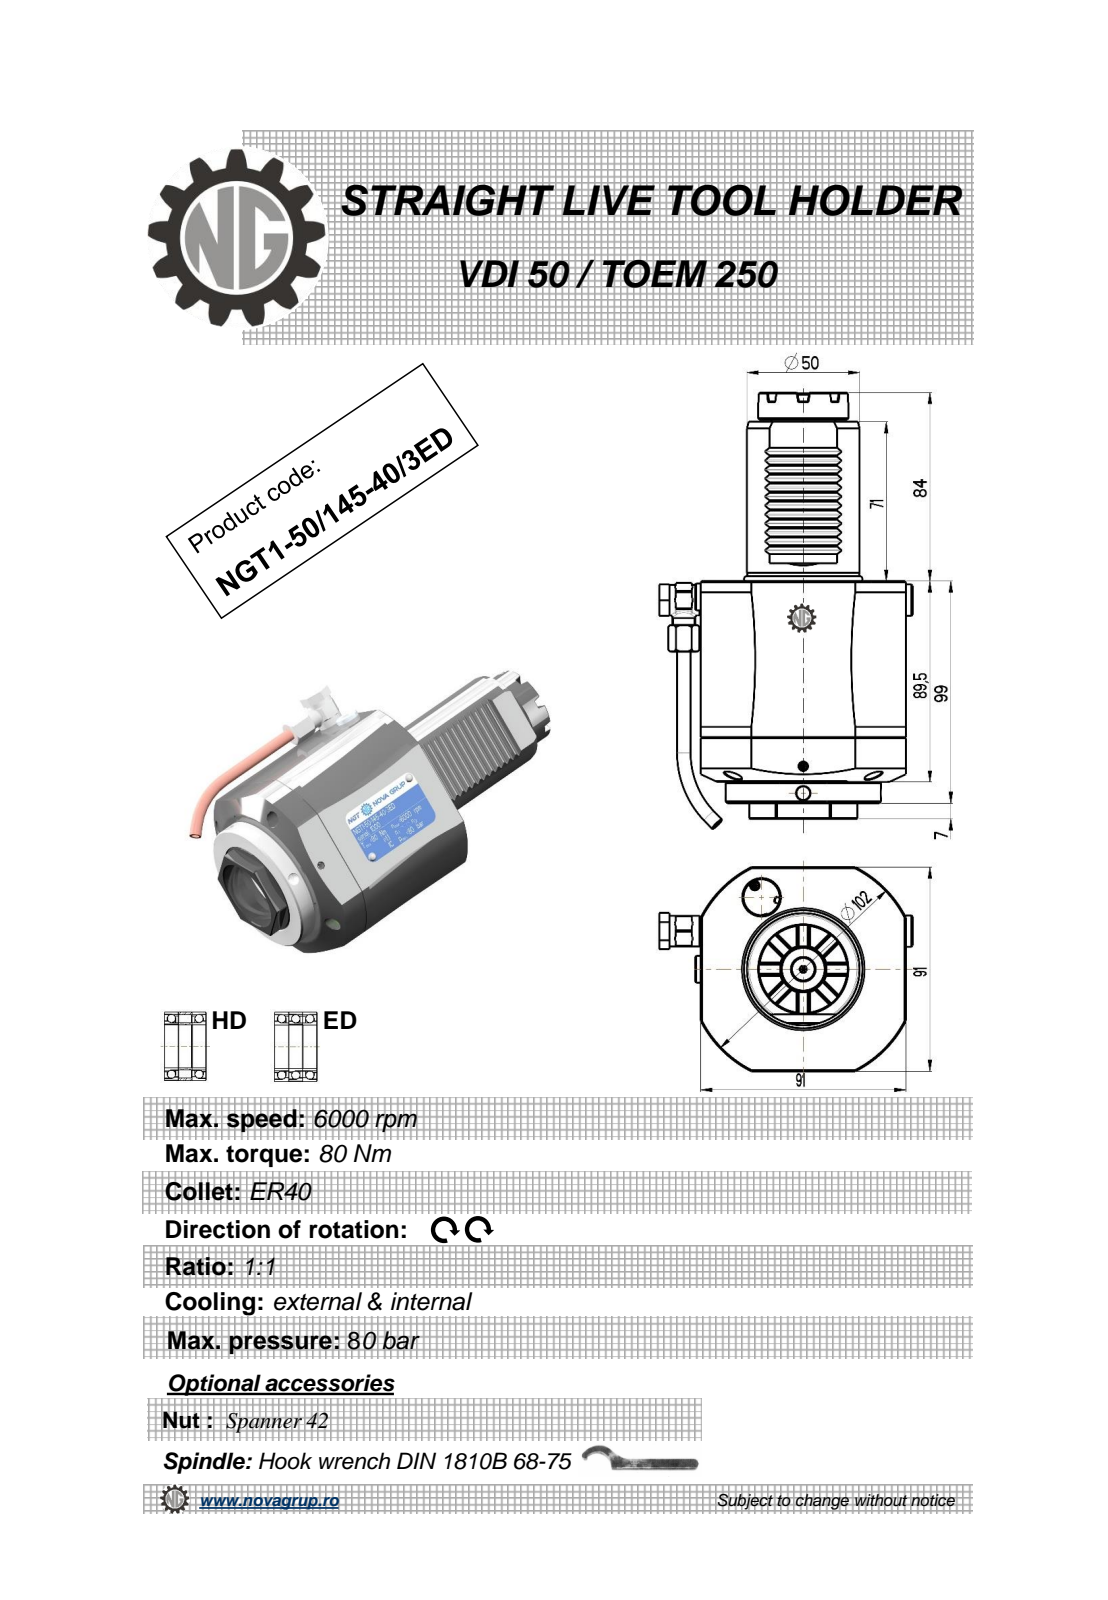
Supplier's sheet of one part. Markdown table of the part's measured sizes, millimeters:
| quantity | value |
| --- | --- |
| part name | NGT1_50_145_40_3HD |
| STEP written by | PRO/ENGINEER BY PARAMETRIC TECHNOLOGY CORPORATION, 2010280 (CONFIG_CONTROL_DESIGN) |
| units | millimeters |
| bodies | 1 solid, 438 faces (184 planar, 102 cylindrical, 152 other) |
| overall size | 194.44 × 112.4 × 91 |
| volume | 837 143 mm³ |
| surface area | 68 515 mm² |
| round holes (diameter × count) | 4 × 3, 6 × 2, 3 × 1, 6.2 × 1, 9 × 1, 10 × 1, 11 × 1, 36.2 × 1, 42 × 1 |
| round bosses / shafts (diameter × count) | 6 × 2, 69 × 1, 50 × 1, 40 × 1, 20.5 × 1, 14 × 1, 13.6 × 1, 13 × 1 |
| partial cylindrical surfaces (radius × count) | 0.3 × 12, 0.41 × 6, 0.5 × 4, 6.25 × 1, 7.7 × 1, 24 × 1, 51 × 1 |
| main face-to-face distances | 91, 89.5, 9.5, 99, 2.83, 170, 160.5, 71, 14.14, 11.31 |
| hole center spacings | 0.4, 55.66, 56.04, 87.66 |
